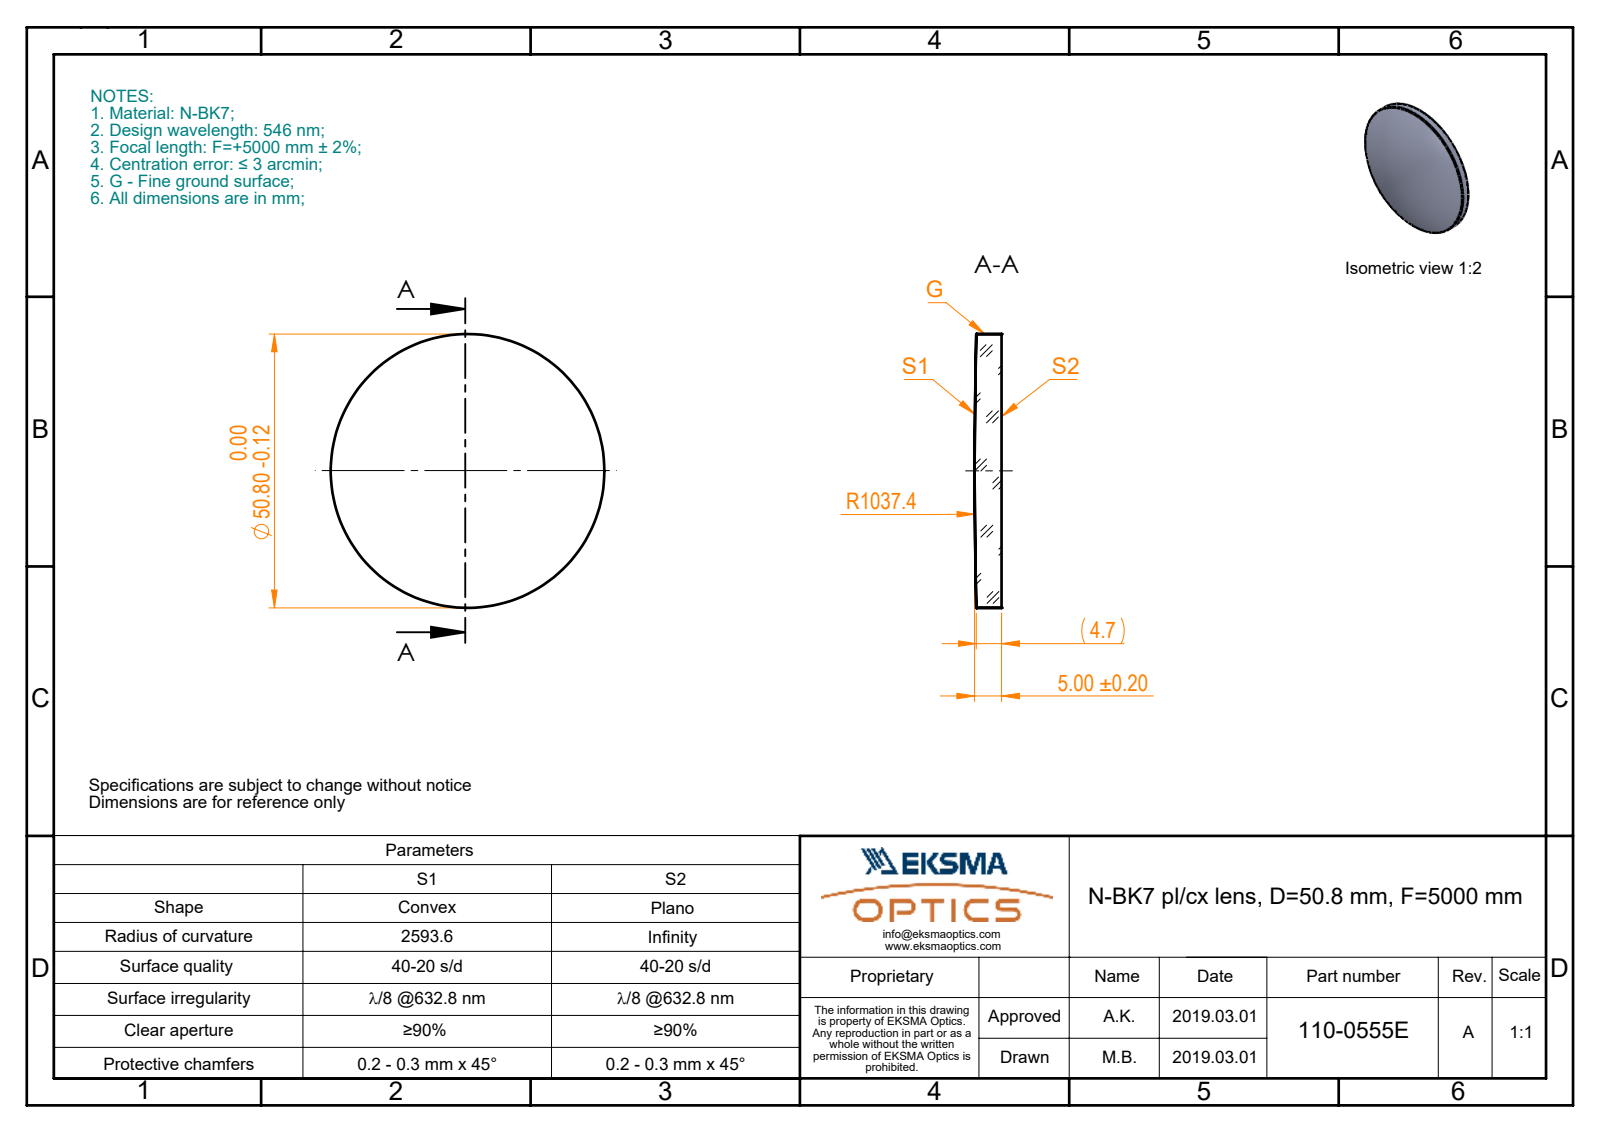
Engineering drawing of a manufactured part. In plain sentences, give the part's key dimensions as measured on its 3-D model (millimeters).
The part is named "110-0555E BK7 pl-cx 50.8 F5000". Its 3-D file was written by "SolidWorks 2017 (CONFIG_CONTROL_DESIGN)". It is 1 solid with 5 faces: 1 planar, 2 cylindrical and 2 other. Overall it measures 50.8 by 50.8 by 5 millimeters. Its volume is 10 008 cubic millimeters and its surface area 4 832 square millimeters. Round bosses or shafts: 1 of diameter 50.8.
